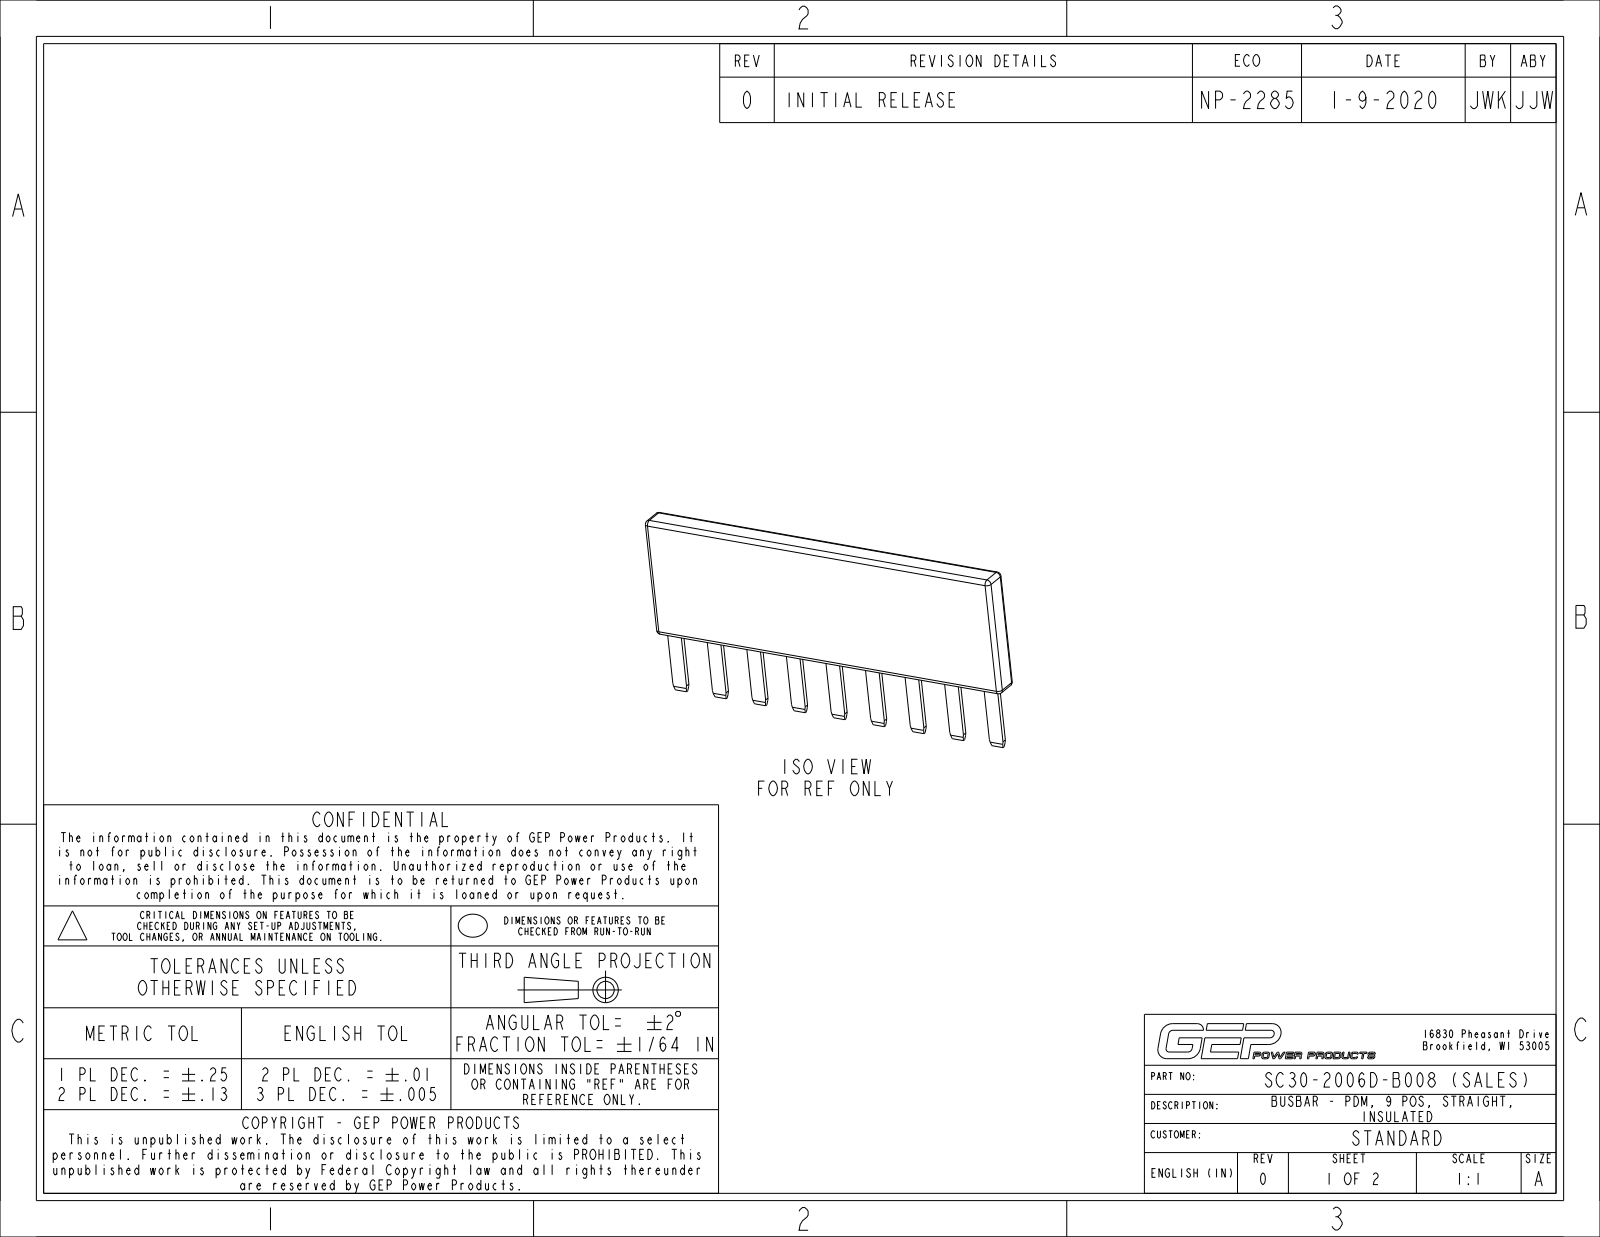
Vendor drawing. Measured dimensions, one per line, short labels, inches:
name: PC30-2006D-B008_MOLD; PC29-2004D-C000_NCF; PC30-2006D-B008_NCF_ASM; SC30-2006D-B008_NCF_ASM
written by: CREO PARAMETRIC BY PTC INC, 2017110 (CONFIG_CONTROL_DESIGN)
unit: in
bodies: 2 solids, 144 faces (122 planar, 14 cylindrical, 8 other)
size: 2.781 × 1.31 × 0.184
volume: 0.456 in³; area: 19.81 in²
rounds: 12× R0.03, 1× R0.032
face distances: 0.06, 0.124, 0.032, 0.032, 0.064, 0.092, 0.184, 0.092, 0.87, 0.319
